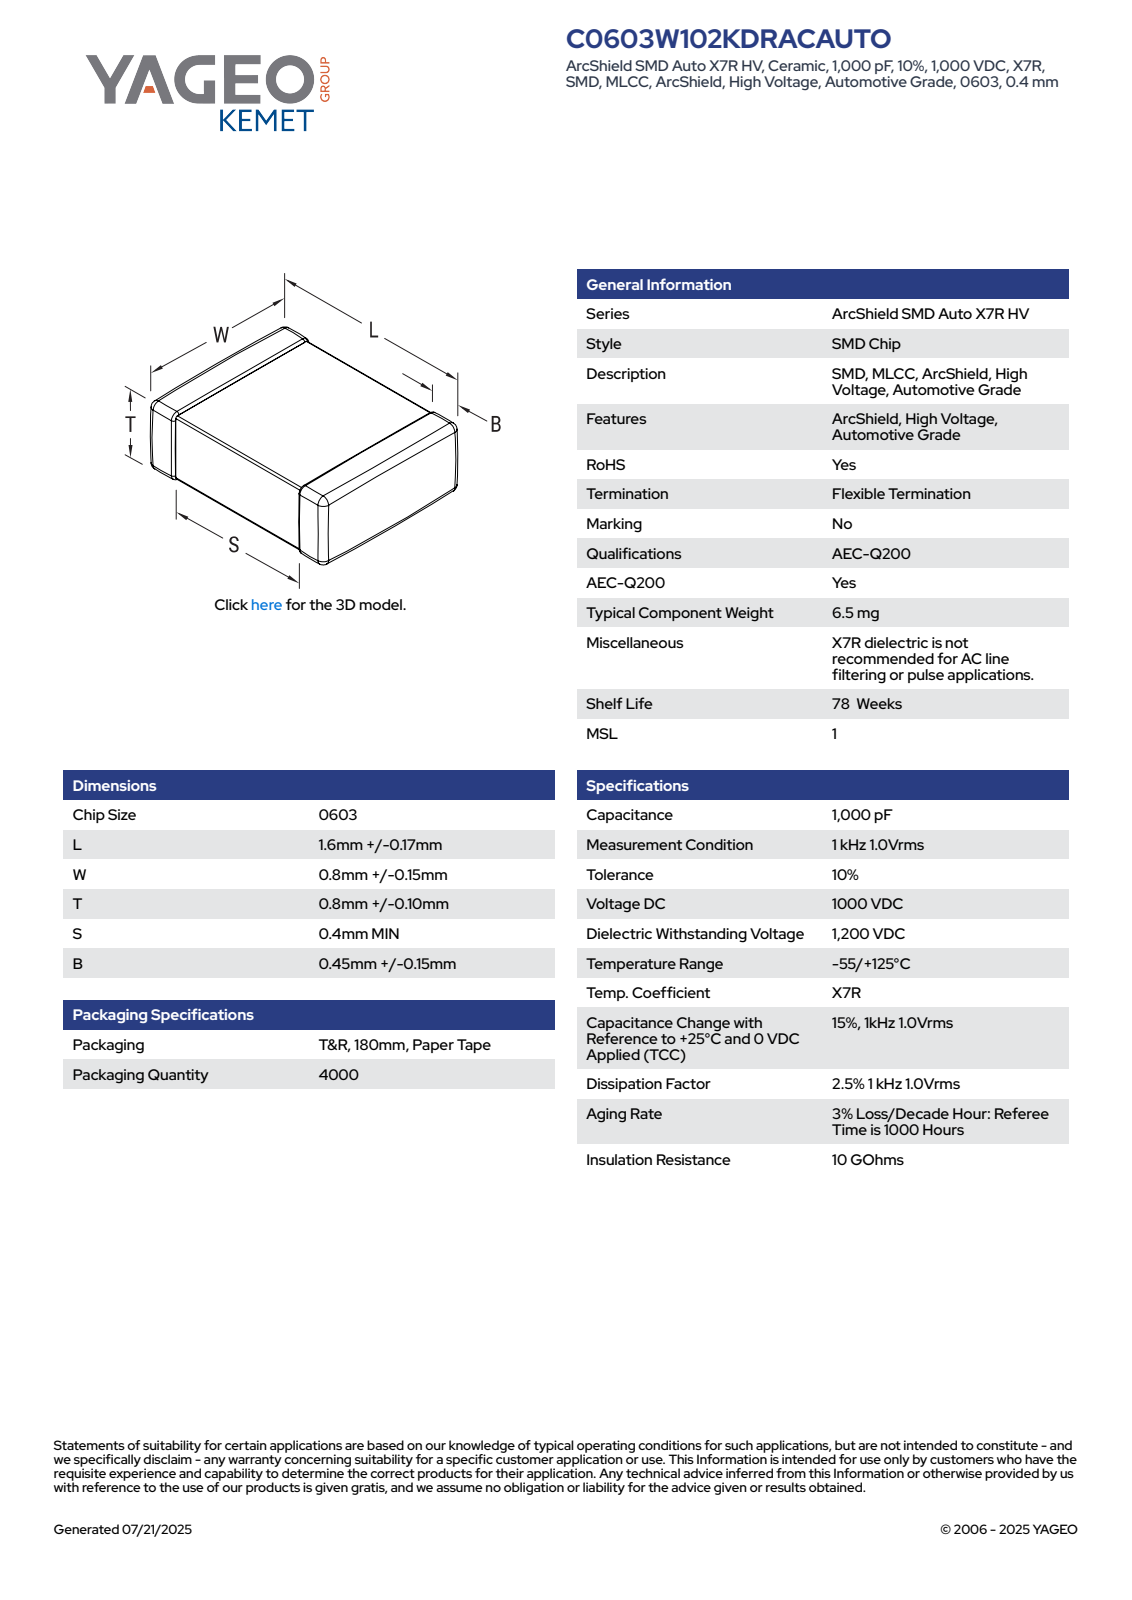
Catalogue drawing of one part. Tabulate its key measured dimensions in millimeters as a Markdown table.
| quantity | value |
| --- | --- |
| part name | CCS_CCSTD_0603_L1.77W0.95T0.9B0.45 |
| STEP written by | SolidWorks 2021 (AUTOMOTIVE_DESIGN) |
| units | millimeters |
| bodies | 4 solids, 125 faces (71 planar, 38 cylindrical, 16 other) |
| overall size | 1.77 × 0.95 × 0.9 |
| volume | 1 mm³ |
| surface area | 8 mm² |
| main face-to-face distances | 0.88, 0.9, 0.95, 0.93, 1.77, 0.86, 0.91, 0.87, 0.89, 0.82 |
